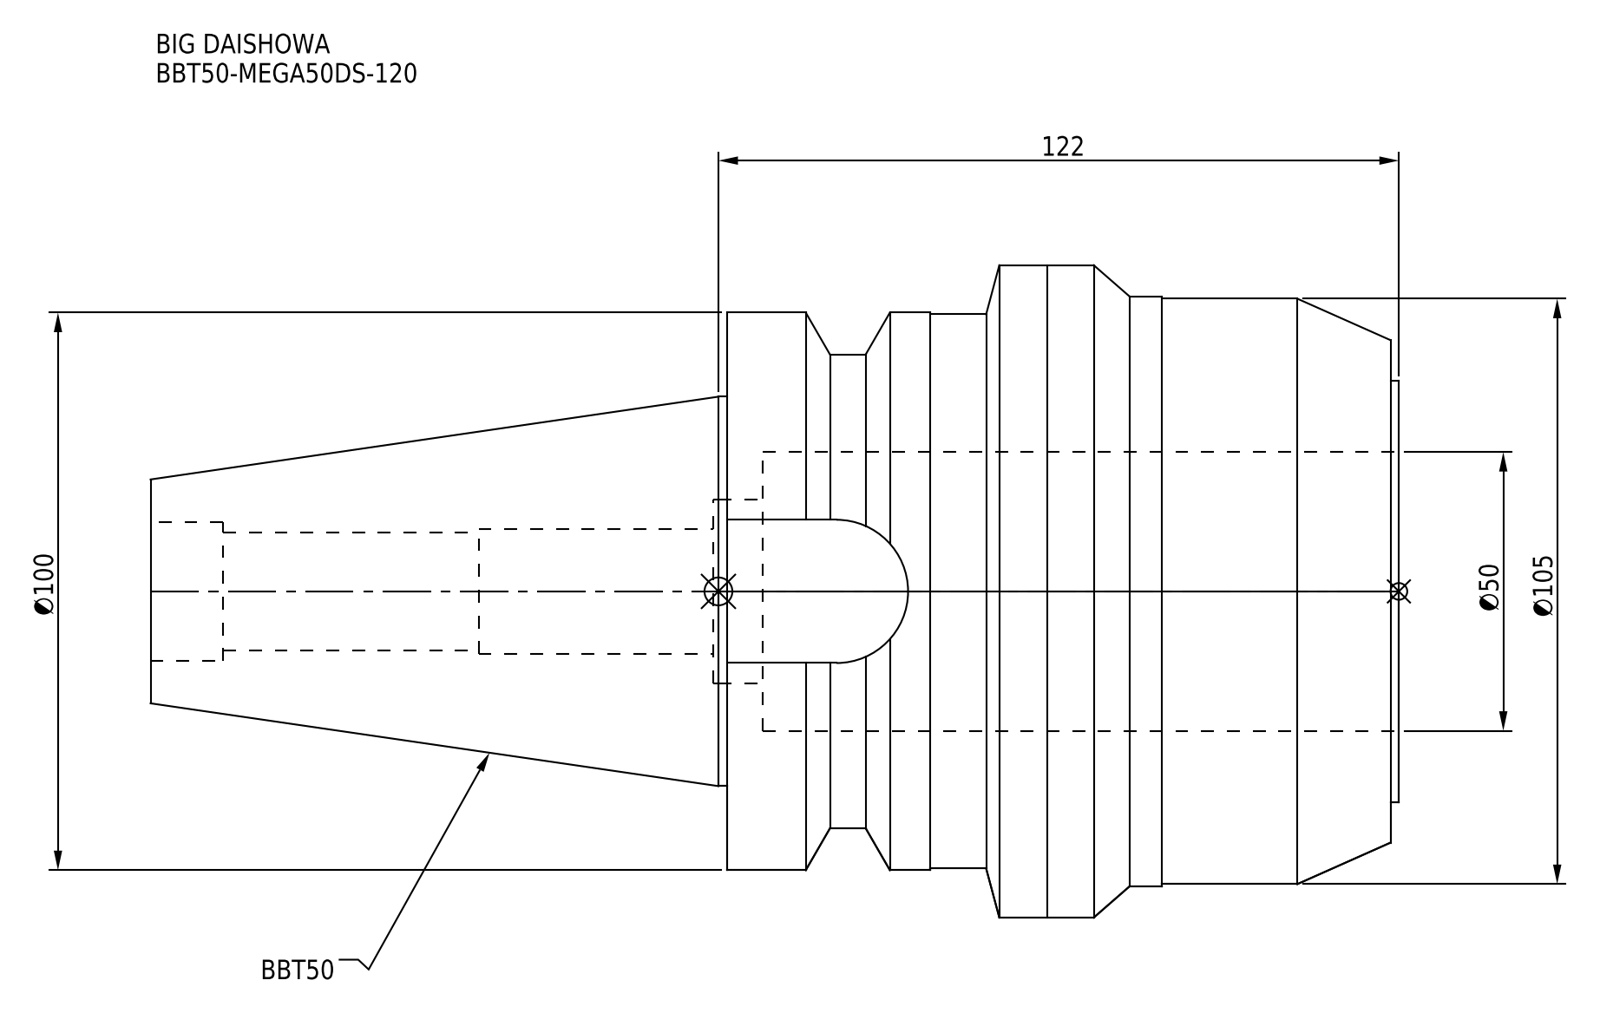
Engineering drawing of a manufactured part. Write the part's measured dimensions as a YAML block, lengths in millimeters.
part_name: "BBT50-MEGA50DS-120"
step_written_by: "CREO PARAMETRIC BY PTC INC, 2016380 (AUTOMOTIVE_DESIGN)"
units: millimeters
bodies: {solids: 1, faces: 60, planar: 16, cylindrical: 32, other: 12}
overall_size: [223.8, 117, 117]
volume: 965244
surface_area: 100594
round_holes:
  - {diameter: 21.2, count: 1}
  - {diameter: 22.5, count: 1}
  - {diameter: 25, count: 1}
  - {diameter: 33, count: 1}
  - {diameter: 50, count: 1}
round_bosses_or_shafts:
  - {diameter: 117, count: 1}
  - {diameter: 105.7, count: 1}
  - {diameter: 105, count: 1}
  - {diameter: 100, count: 1}
  - {diameter: 99.4, count: 1}
  - {diameter: 85, count: 1}
  - {diameter: 75.5, count: 1}
  - {diameter: 69.85, count: 1}
partial_cylinders:
  - {radius: 12.85, count: 1}
face_to_face_distances: [120.5, 1.5, 119, 114, 112.5, 6.5, 223.8, 222.3, 109.8, 103.3]
